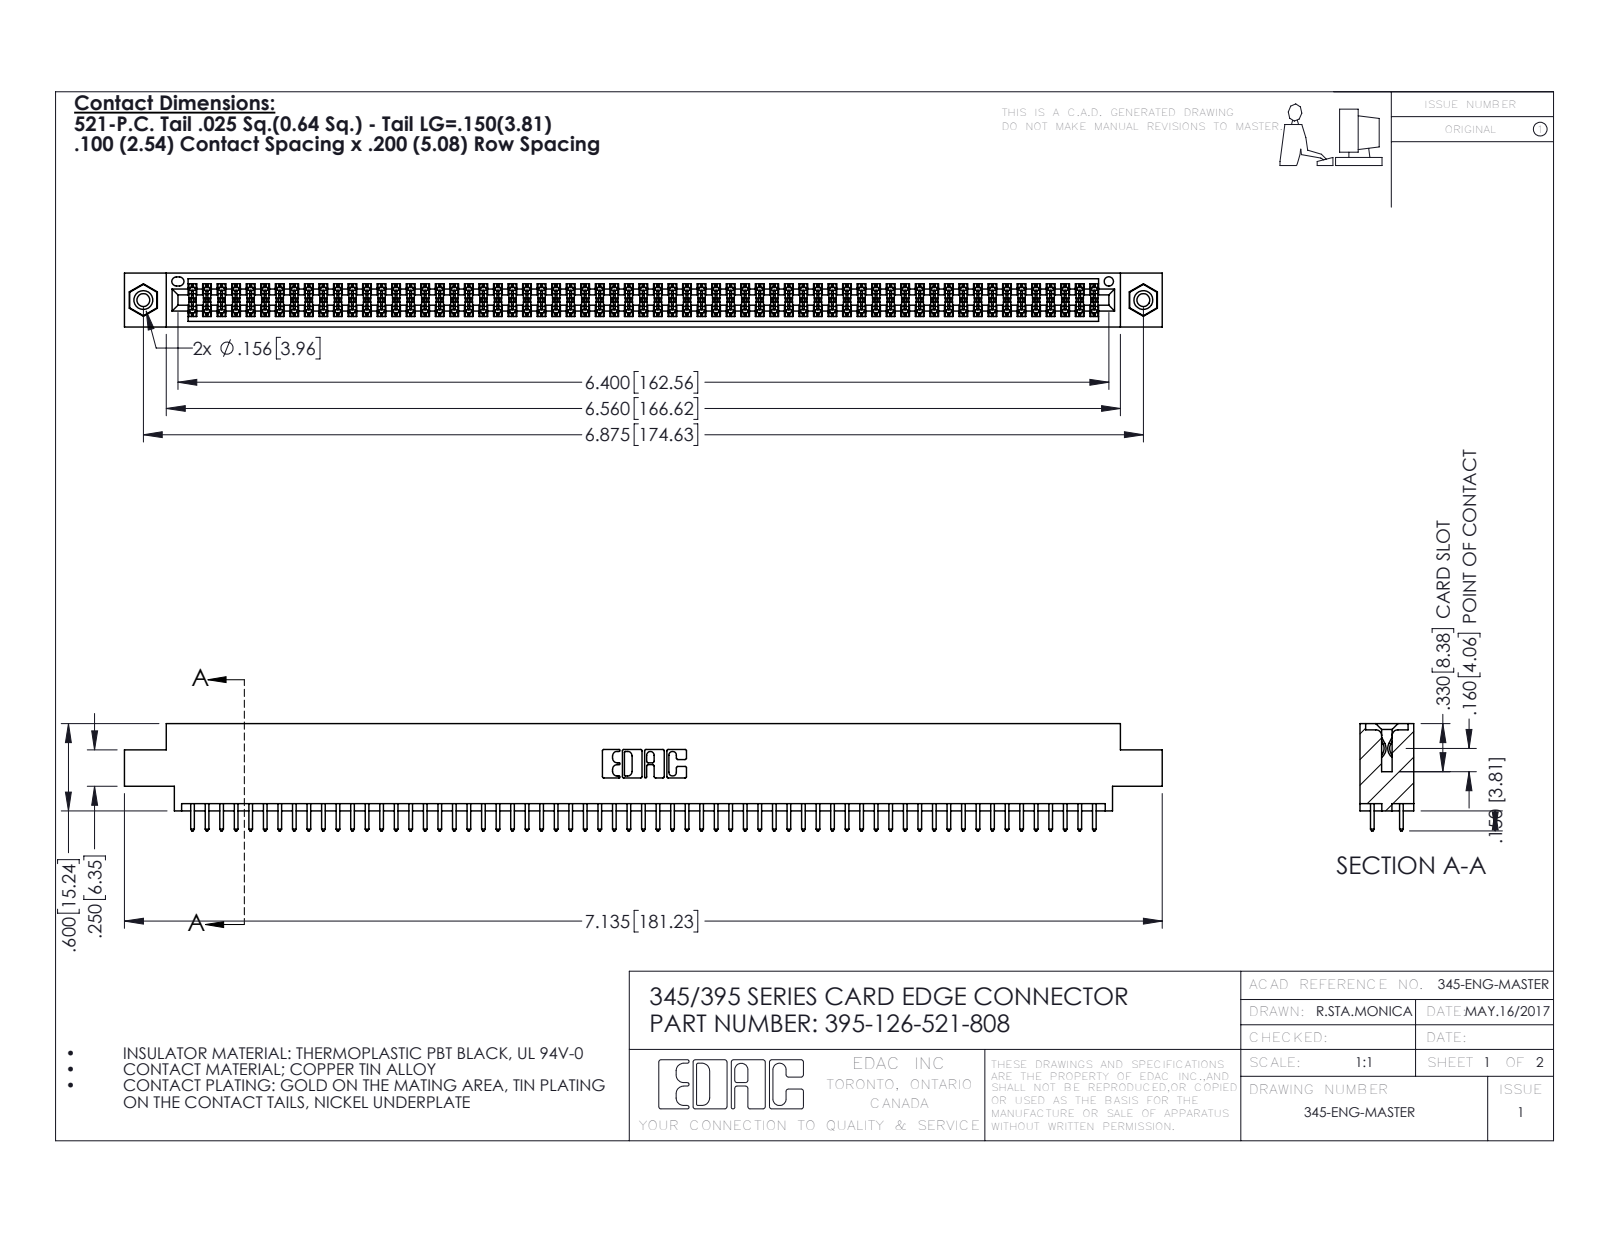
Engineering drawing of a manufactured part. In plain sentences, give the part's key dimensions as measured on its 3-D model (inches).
The part is named "395-126-521-808; 345 Part_0.170 Offset - 0.156 Dia-TI; 345-250-001_345-250-003-102; 345-292-001_345-293-121". Its 3-D file was written by "SolidWorks 2016 (CONFIG_CONTROL_DESIGN)". It is 129 solids with 6490 faces: 4274 planar, 2200 cylindrical and 16 other. Overall it measures 7.135 by 0.737 by 0.37 inches. Its volume is 1.076 cubic inches and its surface area 40.74 square inches. Round holes: 2 of diameter 0.089, 2 of diameter 0.125, 2 of diameter 0.156, 1 of diameter 0.064. Round bosses or shafts: 2 of diameter 0.155. Partial cylindrical surfaces (rounded edges, fillets, slot ends): 189 of radius 0.006, 126 of radius 0.01, 22 of radius 0.01, 6 of radius 0.007, 6 of radius 0.031, 3 of radius 0.026, 2 of radius 0.014, 2 of radius 0.019. The main face-to-face distances are 0.072, 0.298, 0.2, 0.37, 0.098, 0.272, 0.025, 0.225, 0.175, 0.149. The hole center spacings are 0.27, 6.639, 6.875.
